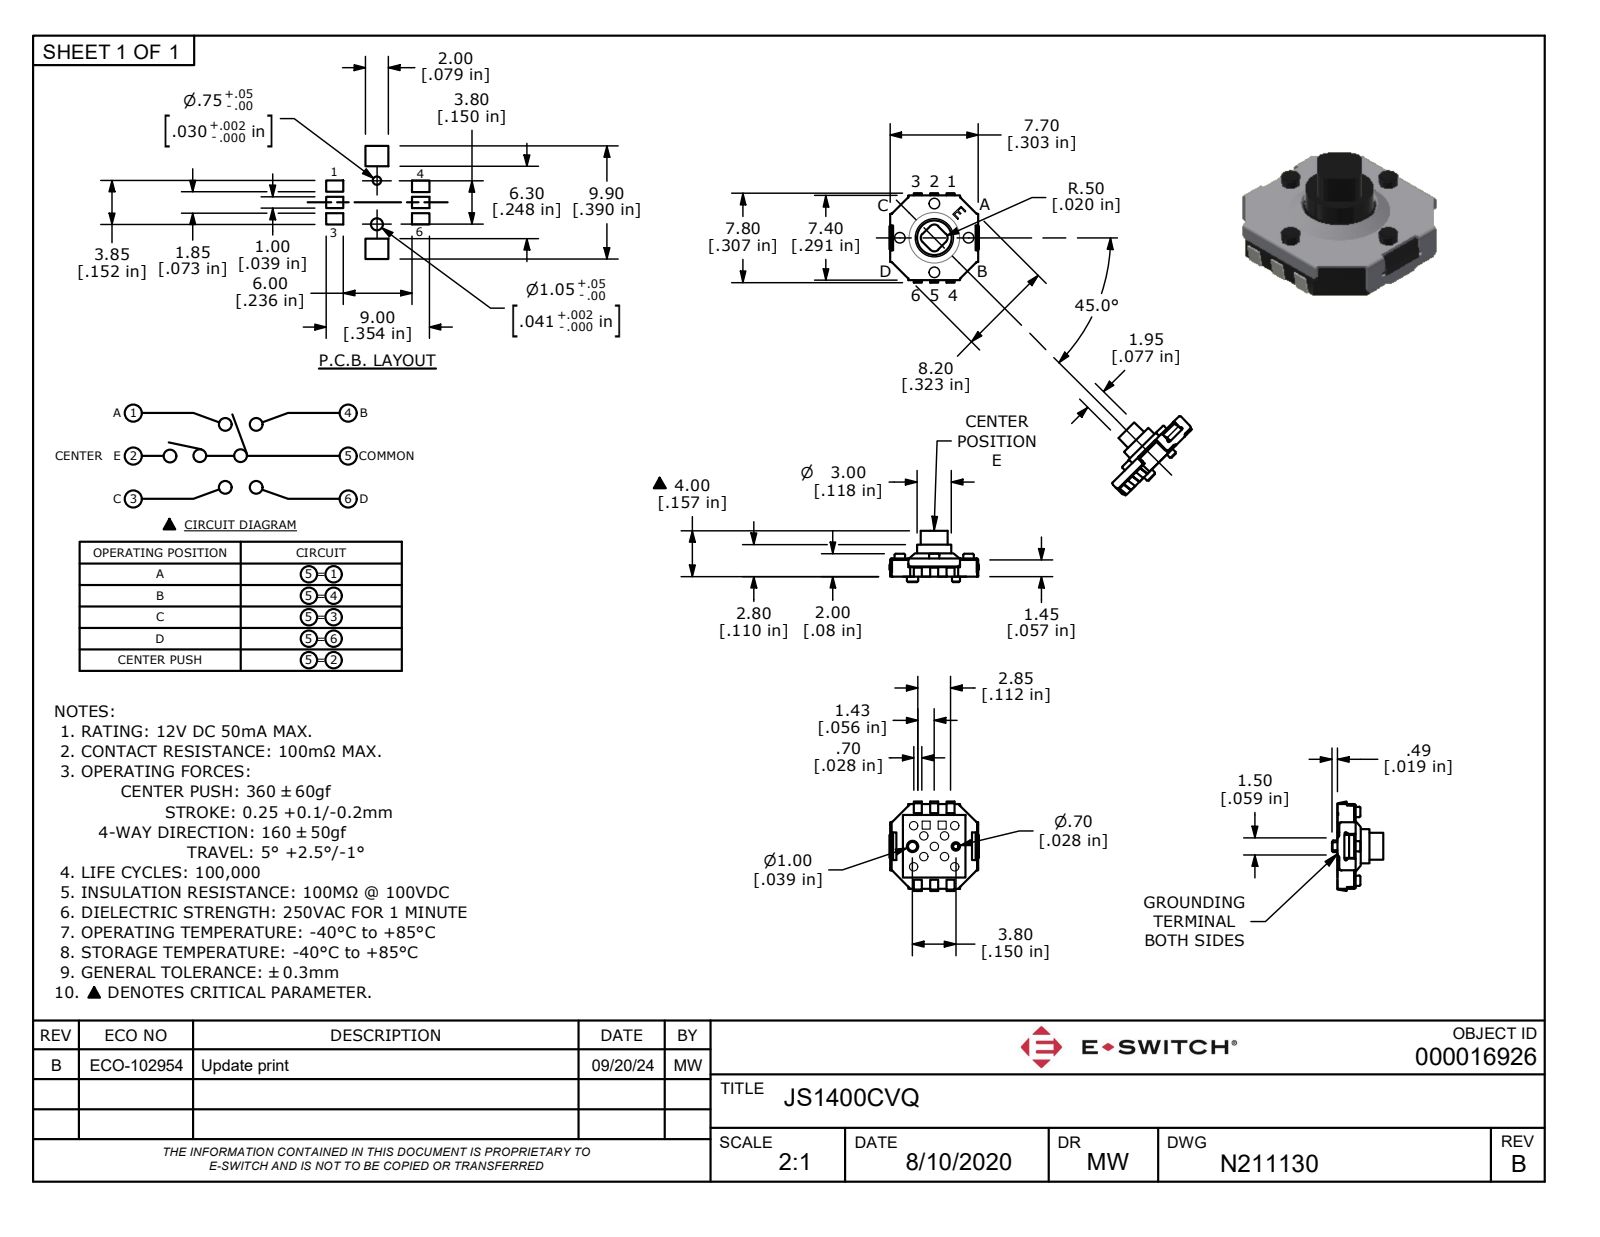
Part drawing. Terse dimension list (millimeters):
name: P:\\E-Switch Secure\\3D_MODELS_STP_FORMAT\\JS1400CVQ.stp
written by: ACIS (CONFIG_CONTROL_DESIGN)
unit: mm
bodies: 1 solid, 254 faces (199 planar, 44 cylindrical, 11 other)
size: 7.8 × 7.8 × 4.5
volume: 80 mm³; area: 299 mm²
holes: 9× ⌀0.7, 4× ⌀0.8
bosses: 5× ⌀0.7, 4× ⌀0.9, 1× ⌀3, 1× ⌀1
rounds: 4× R0.5, 4× R1.2
face distances: 0.6, 1, 1.6, 1.1, 0.5, 1.6, 1.4, 0.5, 1.1, 0.9
hole spacings: 1.3, 2.2, 2.3, 2.8, 4, 5.1, 2.5, 1.8
